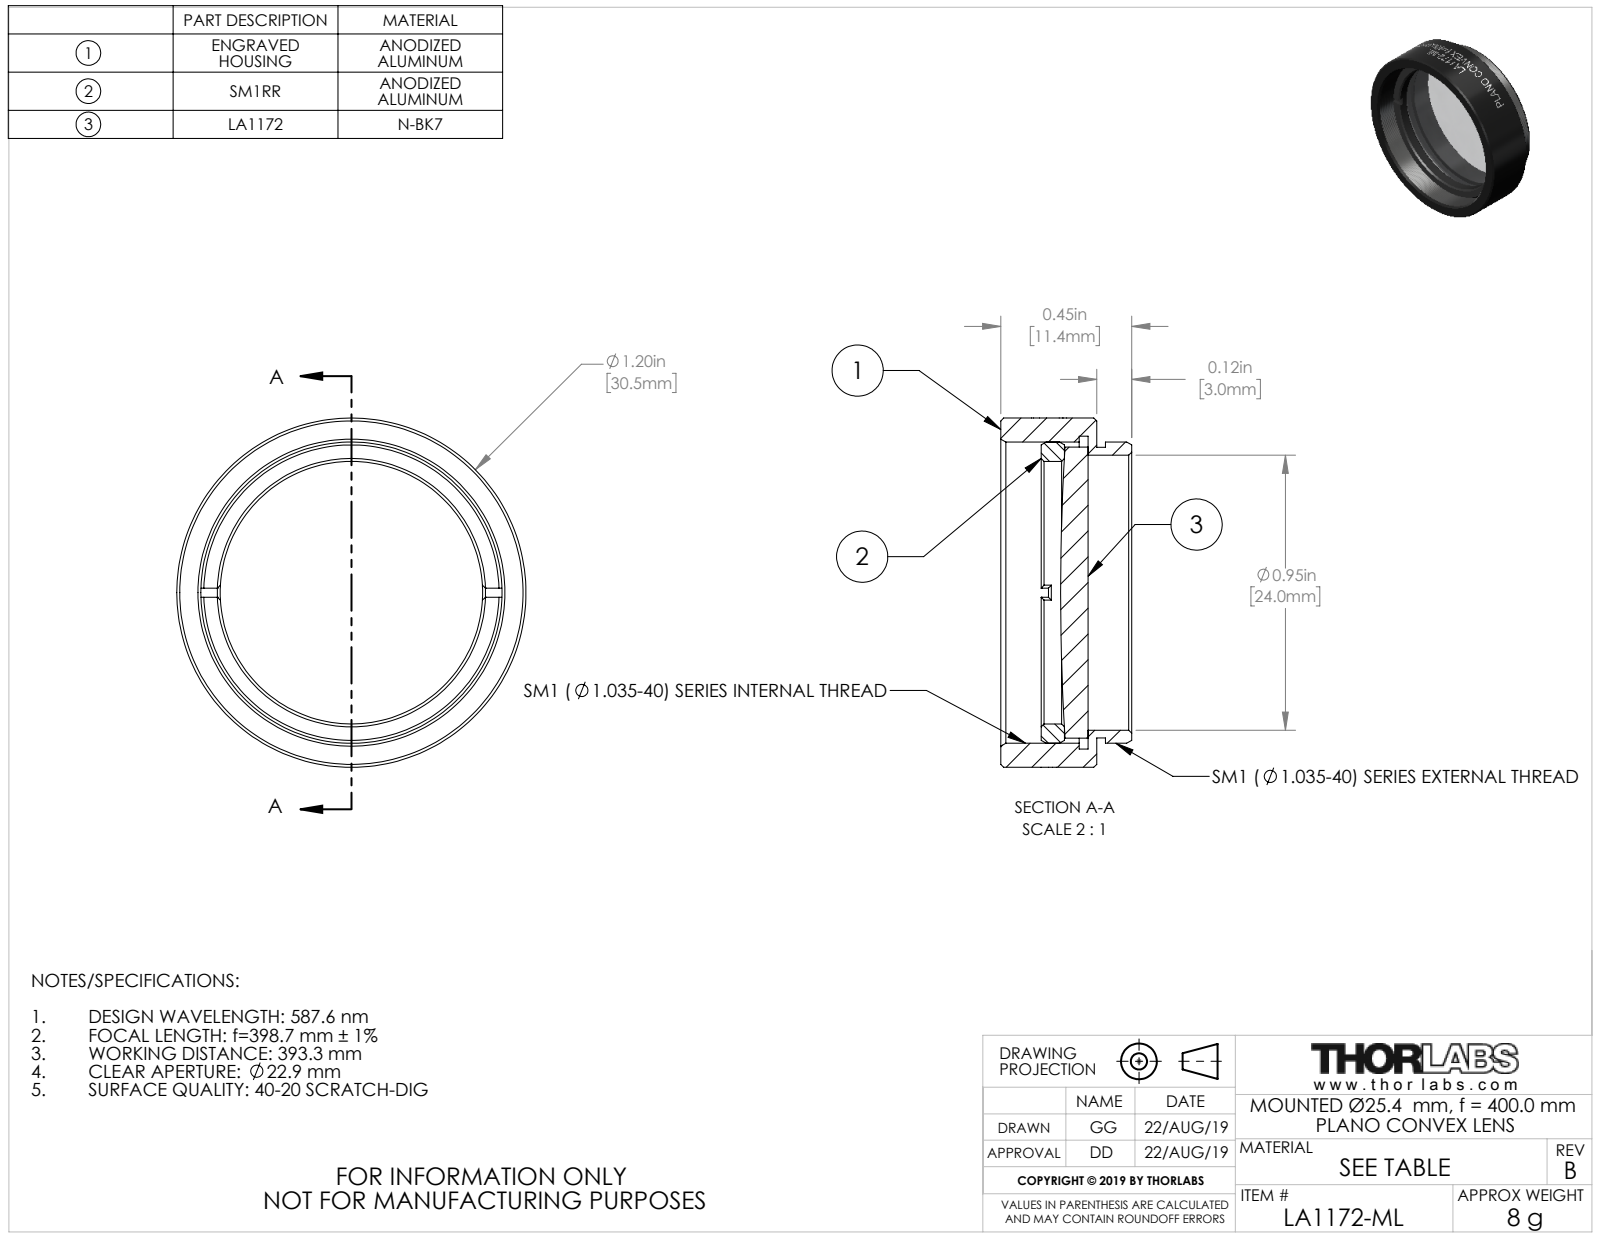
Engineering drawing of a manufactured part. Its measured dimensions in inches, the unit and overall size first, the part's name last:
Units: inches
Overall size (bounding box): 1.2 × 1.2 × 0.45
Round holes (diameter × count): ⌀0.902 ×1, ⌀0.945 ×1, ⌀1.075 ×1
Round bosses / shafts (diameter × count): ⌀1.2 ×1, ⌀1.035 ×1, ⌀1 ×1, ⌀0.999 ×1
Main face-to-face distances: 0.03, 0.33, 0.3, 0.111, 0.081, 0.219, 0.191, 0.161, 0.08, 0.139
Volume: 0.195 in³ · Surface area: 6.685 in²
Bodies: 3 solids, 118 faces (20 planar, 74 cylindrical, 24 other)
Part name (STEP PRODUCT): 24446-E0W
STEP written by: SolidWorks 2018 (CONFIG_CONTROL_DESIGN)
